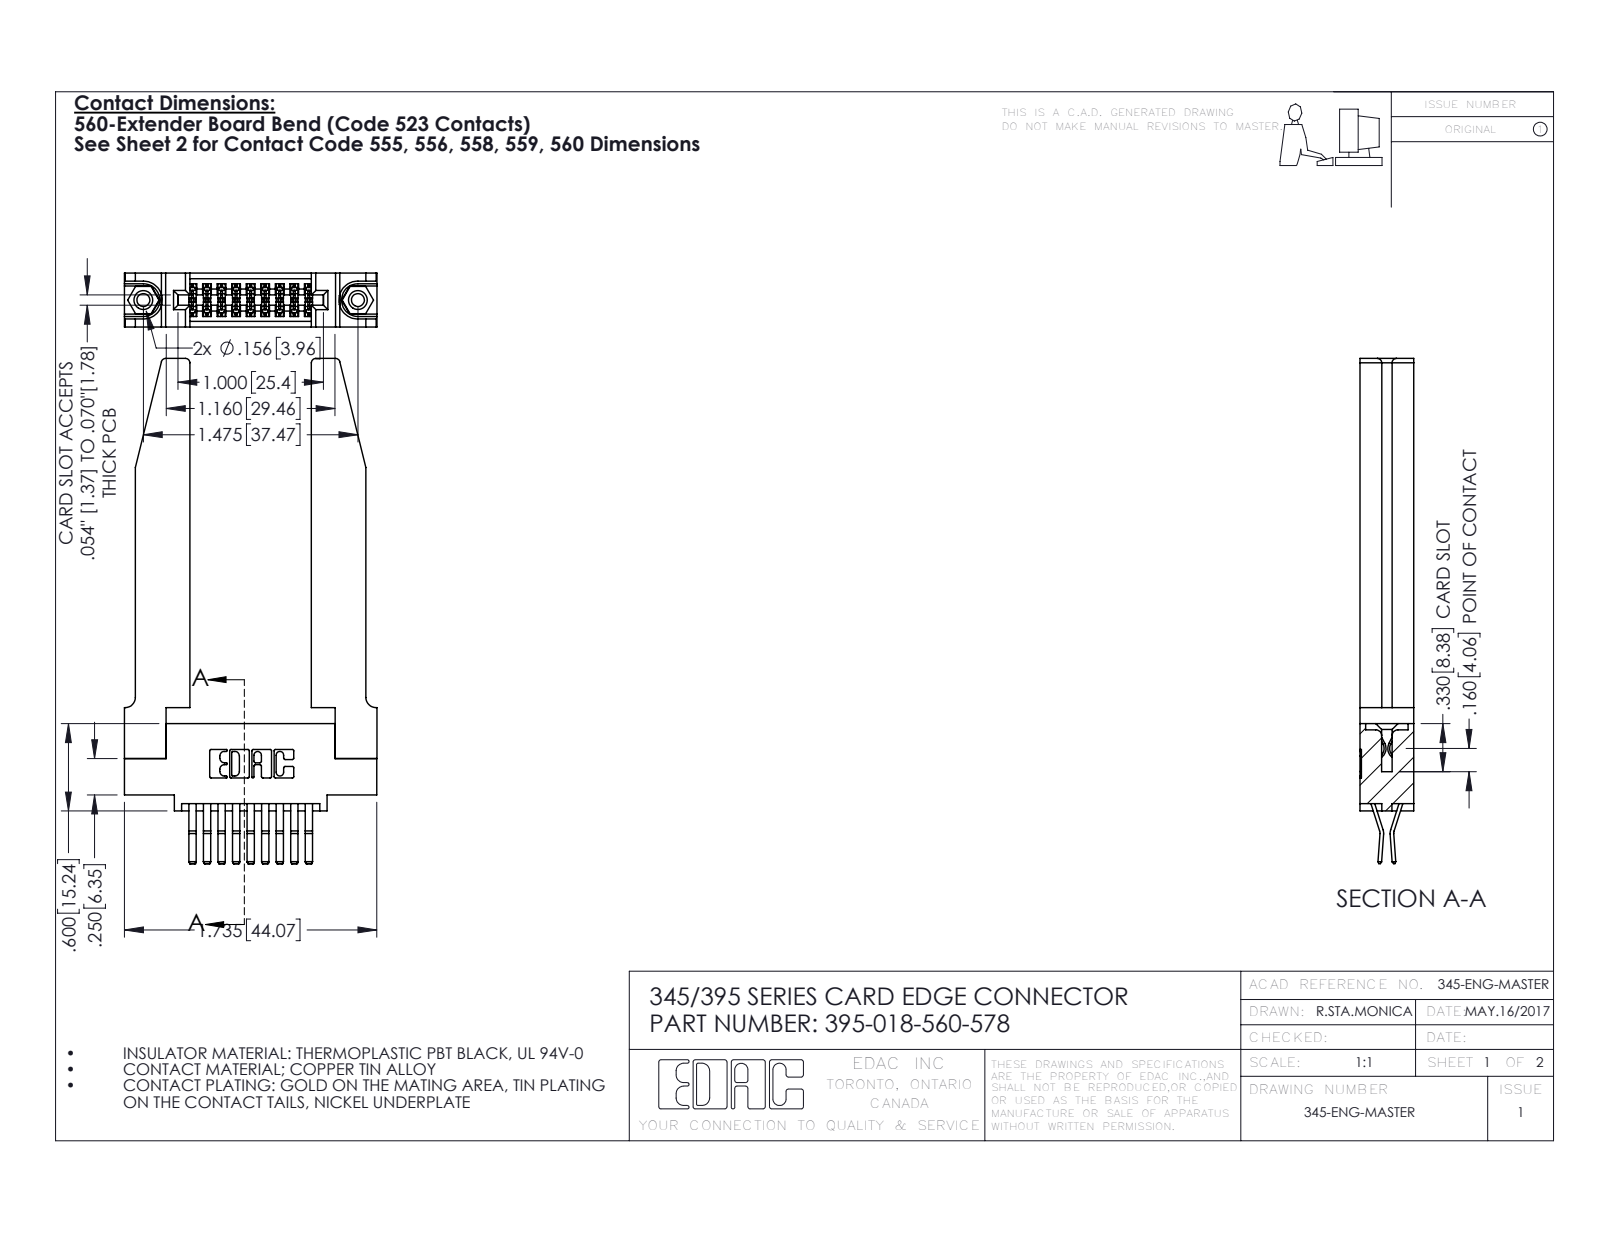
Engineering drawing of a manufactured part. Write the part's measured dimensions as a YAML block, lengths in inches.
part_name: "345 Part_0.110 Offset - 0.156 Dia-TH; 395-018-560-578; 345-292-001_560 Tail; 345-250-001_345-250-001-102 (+1 more)"
step_written_by: "SolidWorks 2016 (CONFIG_CONTROL_DESIGN)"
units: inches
bodies: {solids: 23, faces: 1300, planar: 820, cylindrical: 428, other: 52}
overall_size: [3.472, 1.736, 0.37]
volume: 0.72
surface_area: 19.44
round_holes:
  - {diameter: 0.089, count: 2}
  - {diameter: 0.125, count: 2}
  - {diameter: 0.156, count: 2}
  - {diameter: 0.064, count: 1}
round_bosses_or_shafts:
  - {diameter: 0.155, count: 2}
partial_cylinders:
  - {radius: 0.006, count: 27}
  - {radius: 0.01, count: 22}
  - {radius: 0.03, count: 8}
  - {radius: 0.007, count: 6}
  - {radius: 0.031, count: 6}
  - {radius: 0.026, count: 3}
  - {radius: 0.01, count: 2}
  - {radius: 0.014, count: 2}
face_to_face_distances: [0.37, 0.072, 0.298, 0.148, 0.15, 0.025, 0.22, 0.077, 0.835, 0.225]
hole_center_spacings: [0.27, 1.244, 1.475]
